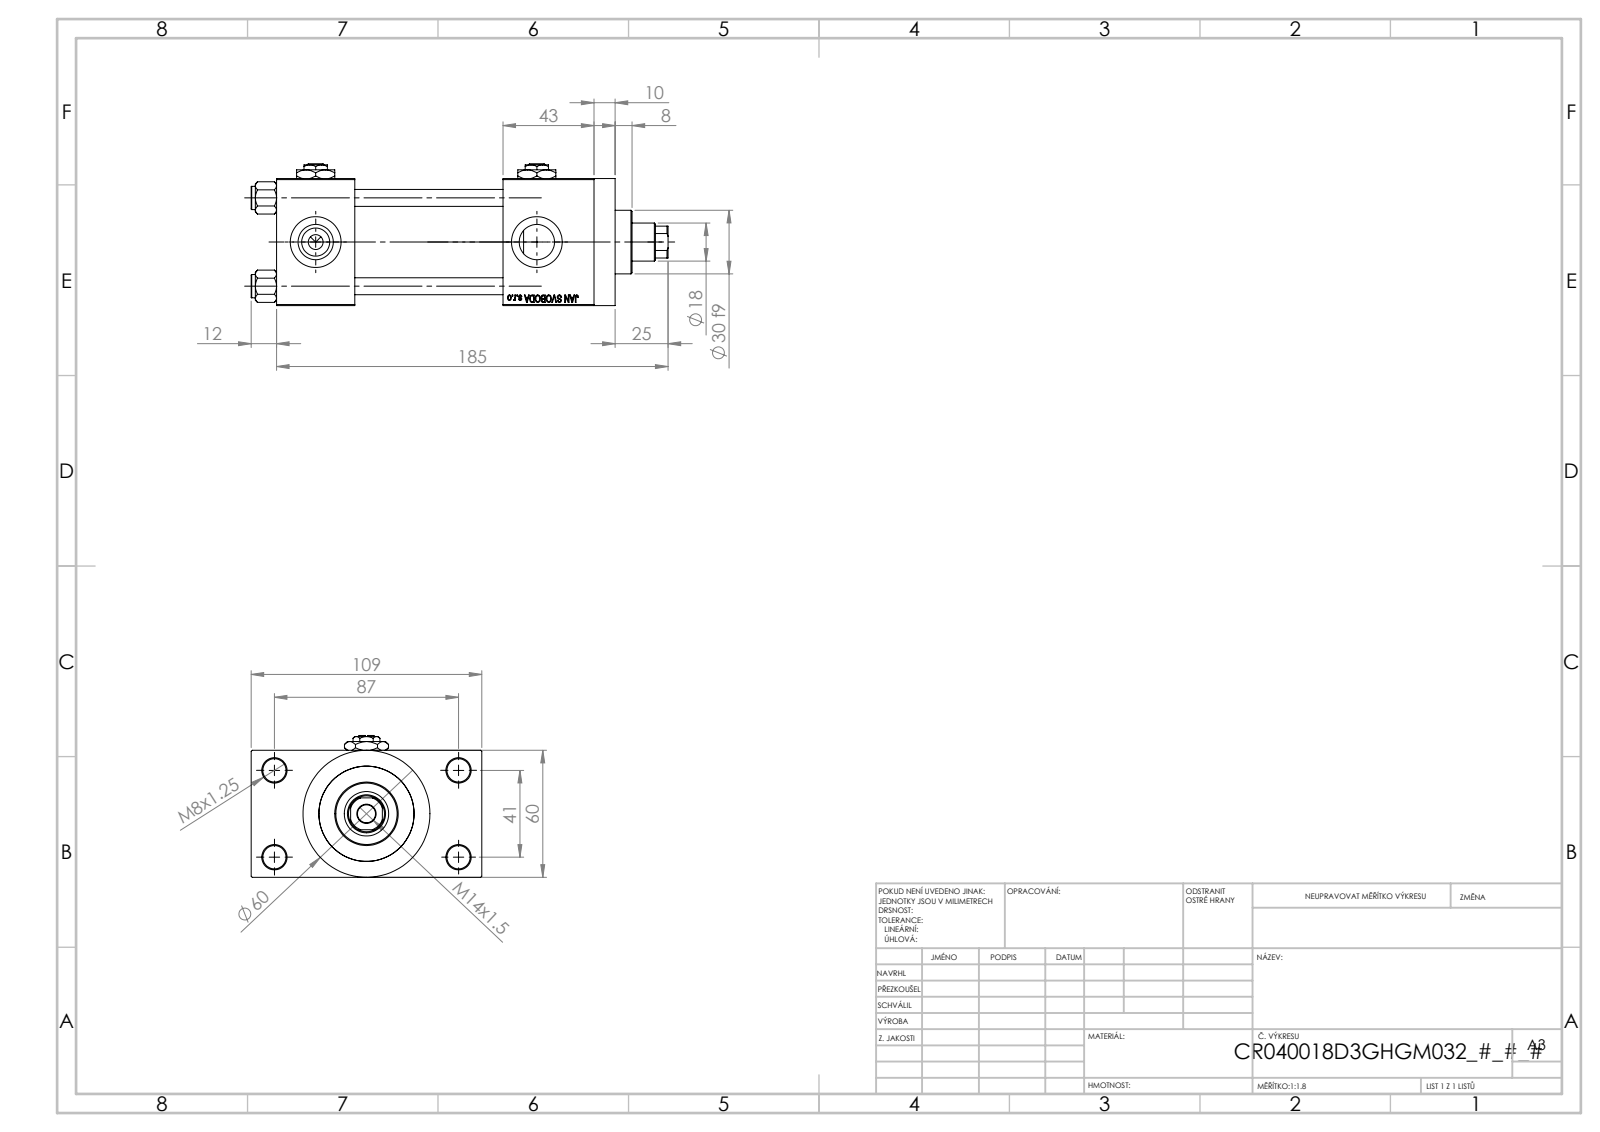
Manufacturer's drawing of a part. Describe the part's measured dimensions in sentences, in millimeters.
The part is named "NUT_M5_D; V215CR_D_TYCINKA; V215CR_VCP_D; V215_VC_A (+2 more)". Its 3-D file was written by "SolidWorks 2019 (CONFIG_CONTROL_DESIGN)". It is 13 solids with 1205 faces: 546 planar, 99 cylindrical and 560 other. Overall it measures 197 by 109 by 67 millimeters. Its volume is 520 667 cubic millimeters and its surface area 130 319 square millimeters. Round holes: 4 of diameter 8, 4 of diameter 11, 4 of diameter 16.66, 4 of diameter 24, 3 of diameter 7, 1 of diameter 8.5, 1 of diameter 18, 1 of diameter 21, 1 of diameter 31, 1 of diameter 40, 1 of diameter 45. Round bosses or shafts: 4 of diameter 11, 1 of diameter 60, 1 of diameter 46, 1 of diameter 30. Partial cylindrical surfaces (rounded edges, fillets, slot ends): 1 of radius 8.5. The main face-to-face distances are 60, 70, 24.5, 84.5, 107, 37, 43, 150, 113, 10. The hole center spacings are 22.65, 29.49, 41.7, 47.15, 48.09, 64.35, 76.49, 41.
